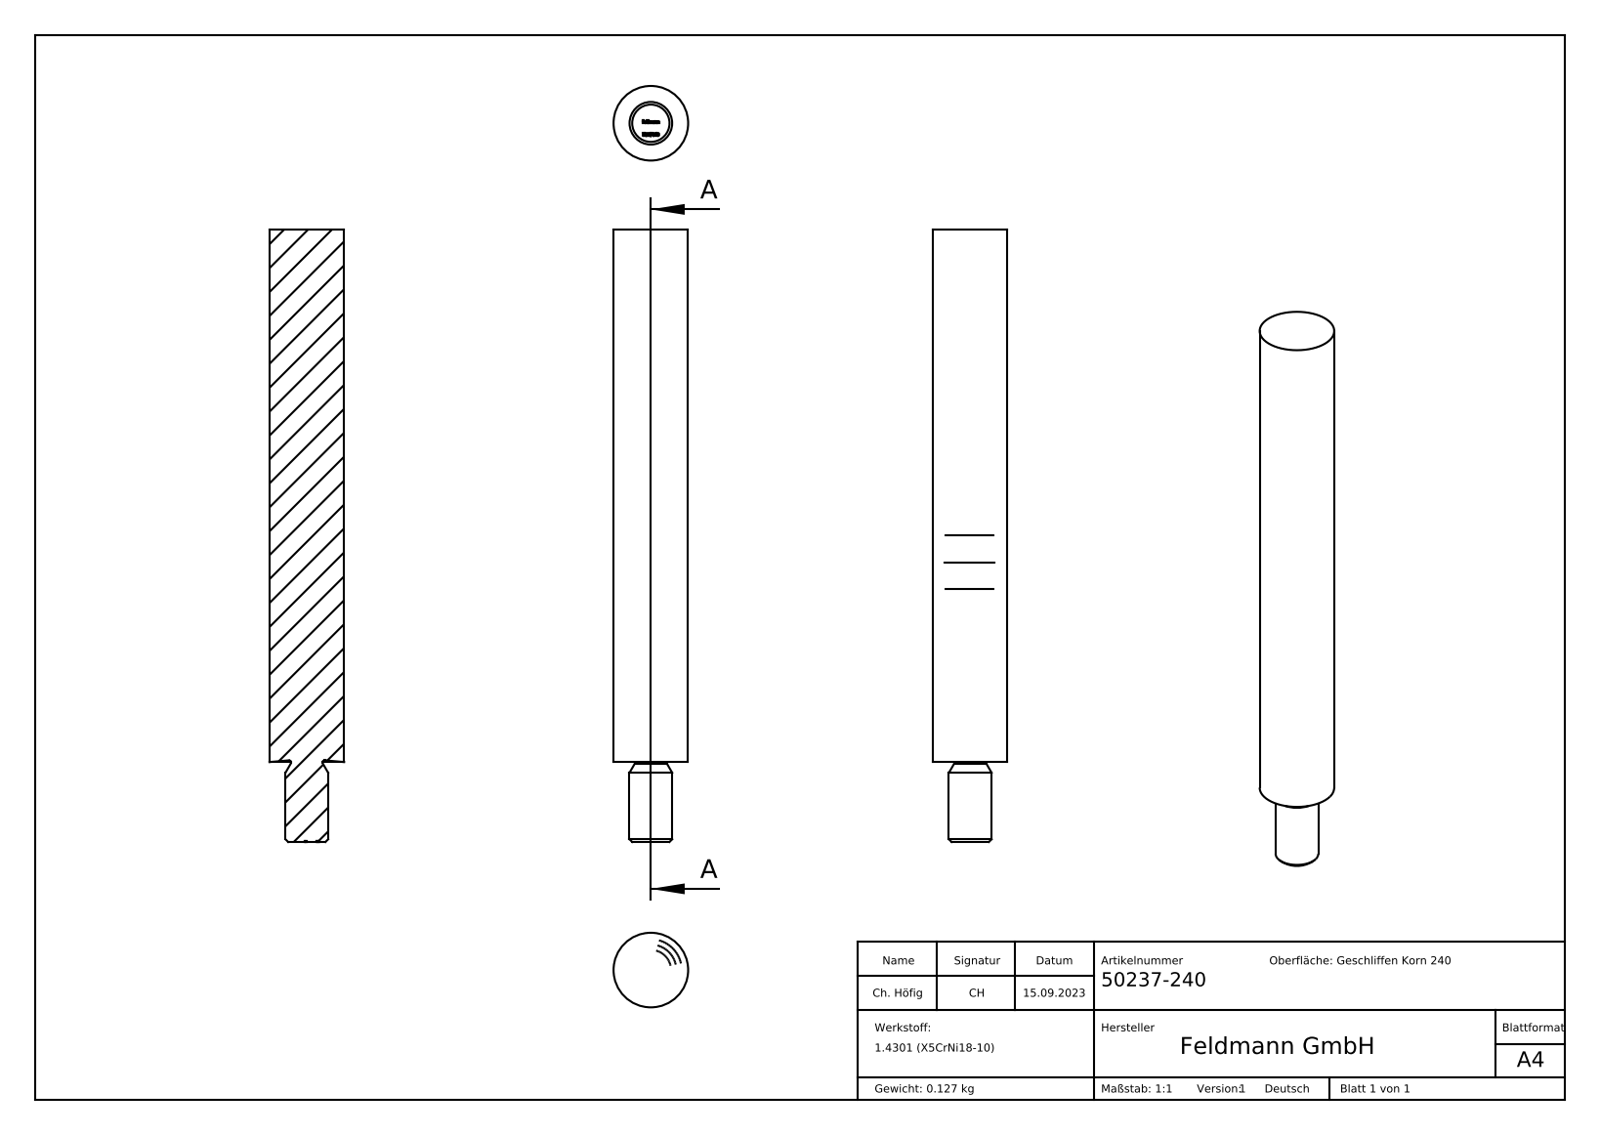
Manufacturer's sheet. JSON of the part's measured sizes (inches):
{"part_name": "50237-240", "step_written_by": "SolidWorks 2018 (CONFIG_CONTROL_DESIGN)", "units": "inches", "bodies": {"solids": 1, "faces": 229, "planar": 123, "cylindrical": 2, "other": 104}, "overall_size": [4.528, 0.551, 0.551], "volume_in3": 0.982, "surface_area_in2": 7.911, "round_bosses_or_shafts": [[0.551, 1], [0.315, 1]], "face_to_face_distances": [4.528, 4.524, 0.075, 0.059, 0.021, 0.094, 0.106, 0.096, 0.022, 0.057]}
